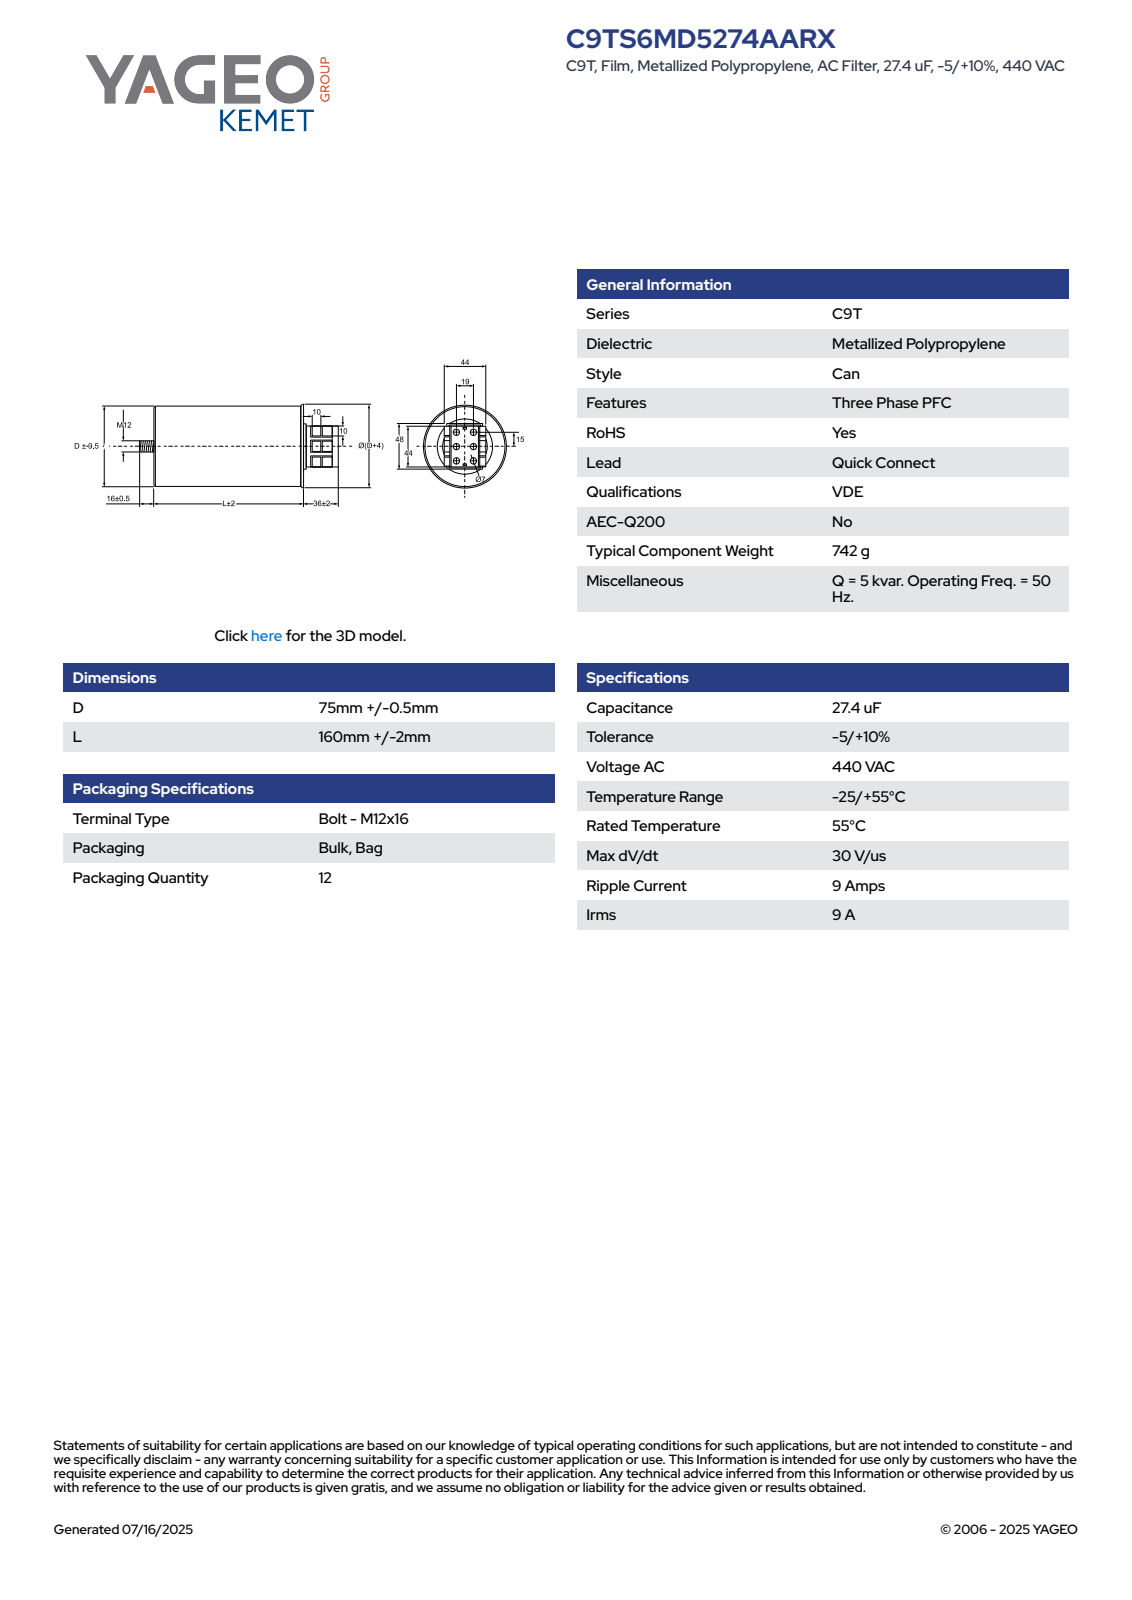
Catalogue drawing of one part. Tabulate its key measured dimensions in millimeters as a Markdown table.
| quantity | value |
| --- | --- |
| part name | CFP_C9T_75X160_D75.5L162 |
| STEP written by | SolidWorks 2014 (AUTOMOTIVE_DESIGN) |
| units | millimeters |
| bodies | 1 solid, 132 faces (78 planar, 19 cylindrical, 35 other) |
| overall size | 216.5 × 79.5 × 79.5 |
| volume | 762 006 mm³ |
| surface area | 69 656 mm² |
| round holes (diameter × count) | 7 × 6 |
| round bosses / shafts (diameter × count) | 75.5 × 1, 12 × 1 |
| partial cylindrical surfaces (radius × count) | 37.76 × 1 |
| main face-to-face distances | 10, 11.15, 162, 15.85, 1.15, 4, 44, 166, 38, 17 |
| hole center spacings | 15, 24.21, 19, 30, 35.51 |
